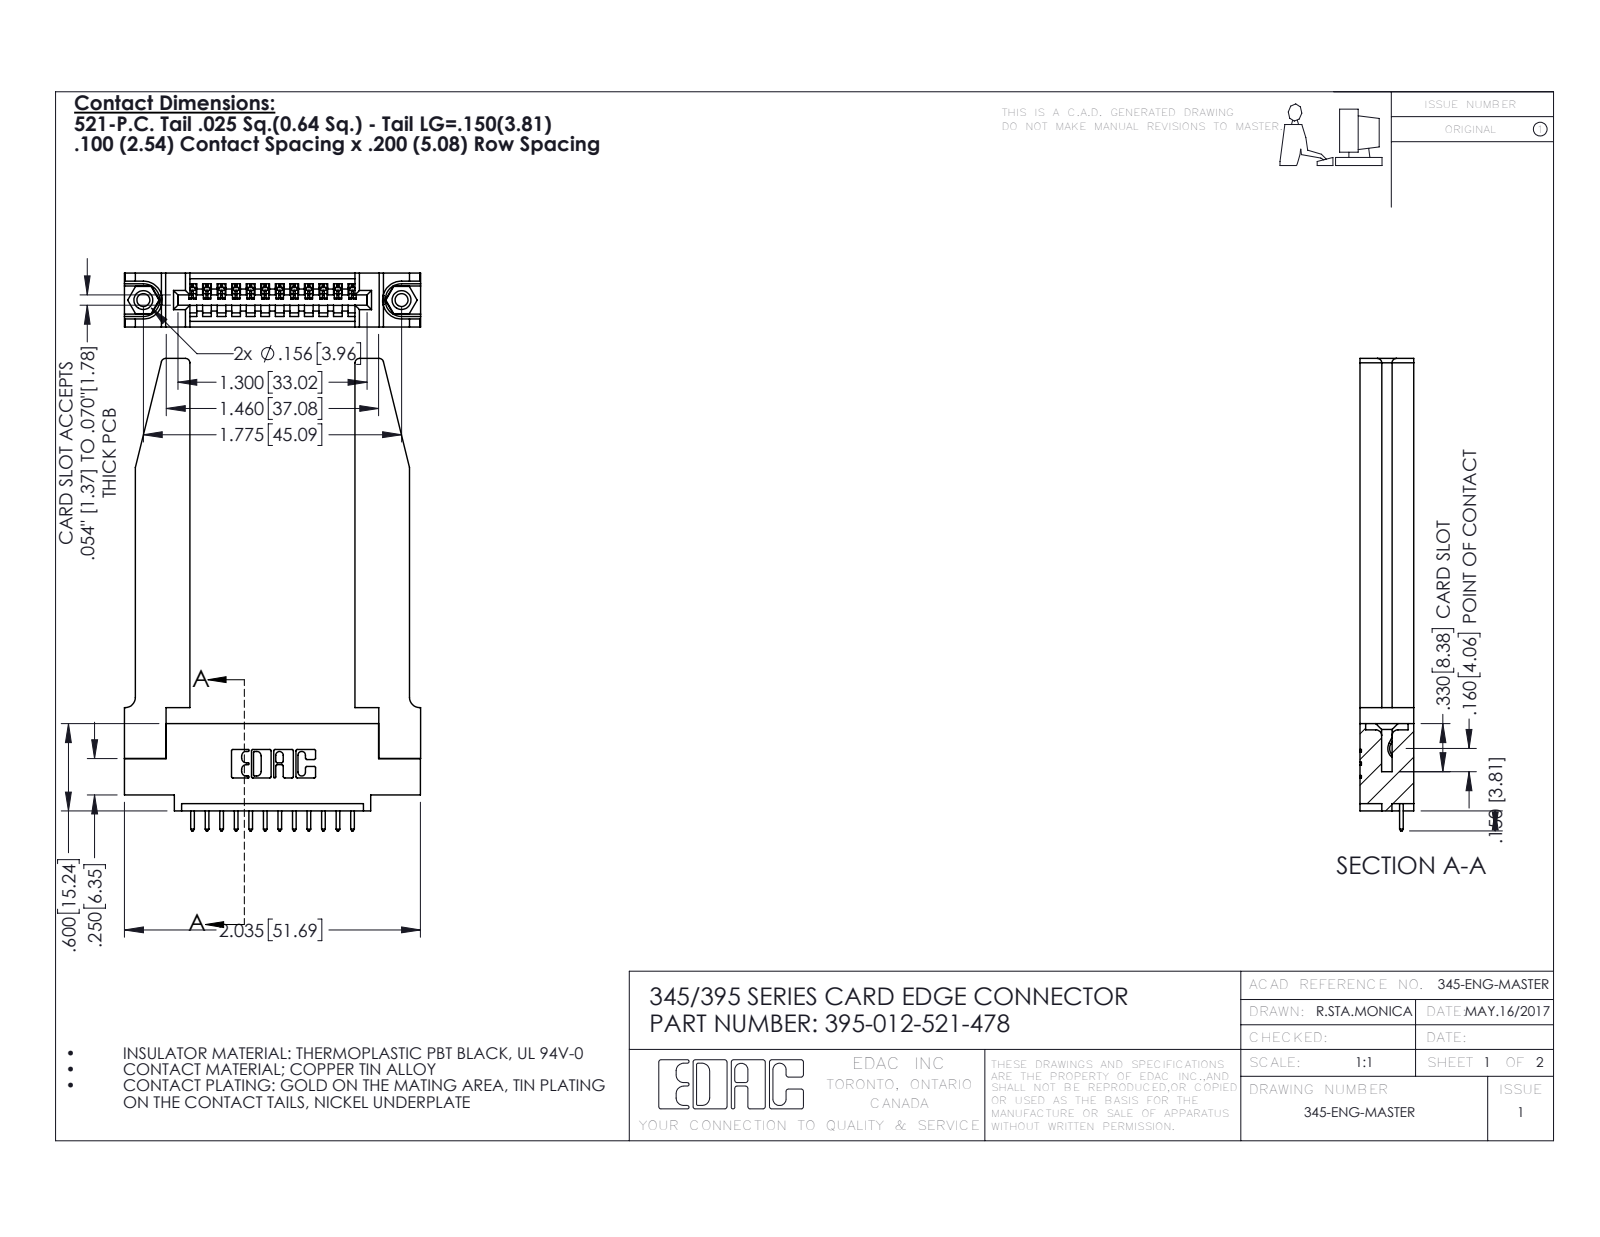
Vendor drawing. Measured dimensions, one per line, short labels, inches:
name: 345-250-001_345-250-001-102; 345 Part_0.110 Offset - 0.156 Dia-TH; 345-220-078_345-220-078; 395-012-521-478 (+1 more)
written by: SolidWorks 2016 (CONFIG_CONTROL_DESIGN)
unit: in
bodies: 17 solids, 1060 faces (706 planar, 302 cylindrical, 52 other)
size: 3.247 × 2.036 × 0.37
volume: 0.752 in³; area: 19.29 in²
holes: 2× ⌀0.089, 2× ⌀0.125, 2× ⌀0.156, 1× ⌀0.064
bosses: 2× ⌀0.155
rounds: 24× R0.006, 24× R0.01, 22× R0.01, 8× R0.03, 6× R0.007, 6× R0.031, 3× R0.026, 2× R0.031
face distances: 0.37, 0.072, 0.298, 0.15, 0.148, 0.22, 0.077, 1.135, 0.2, 0.098
hole spacings: 0.27, 1.543, 1.775
